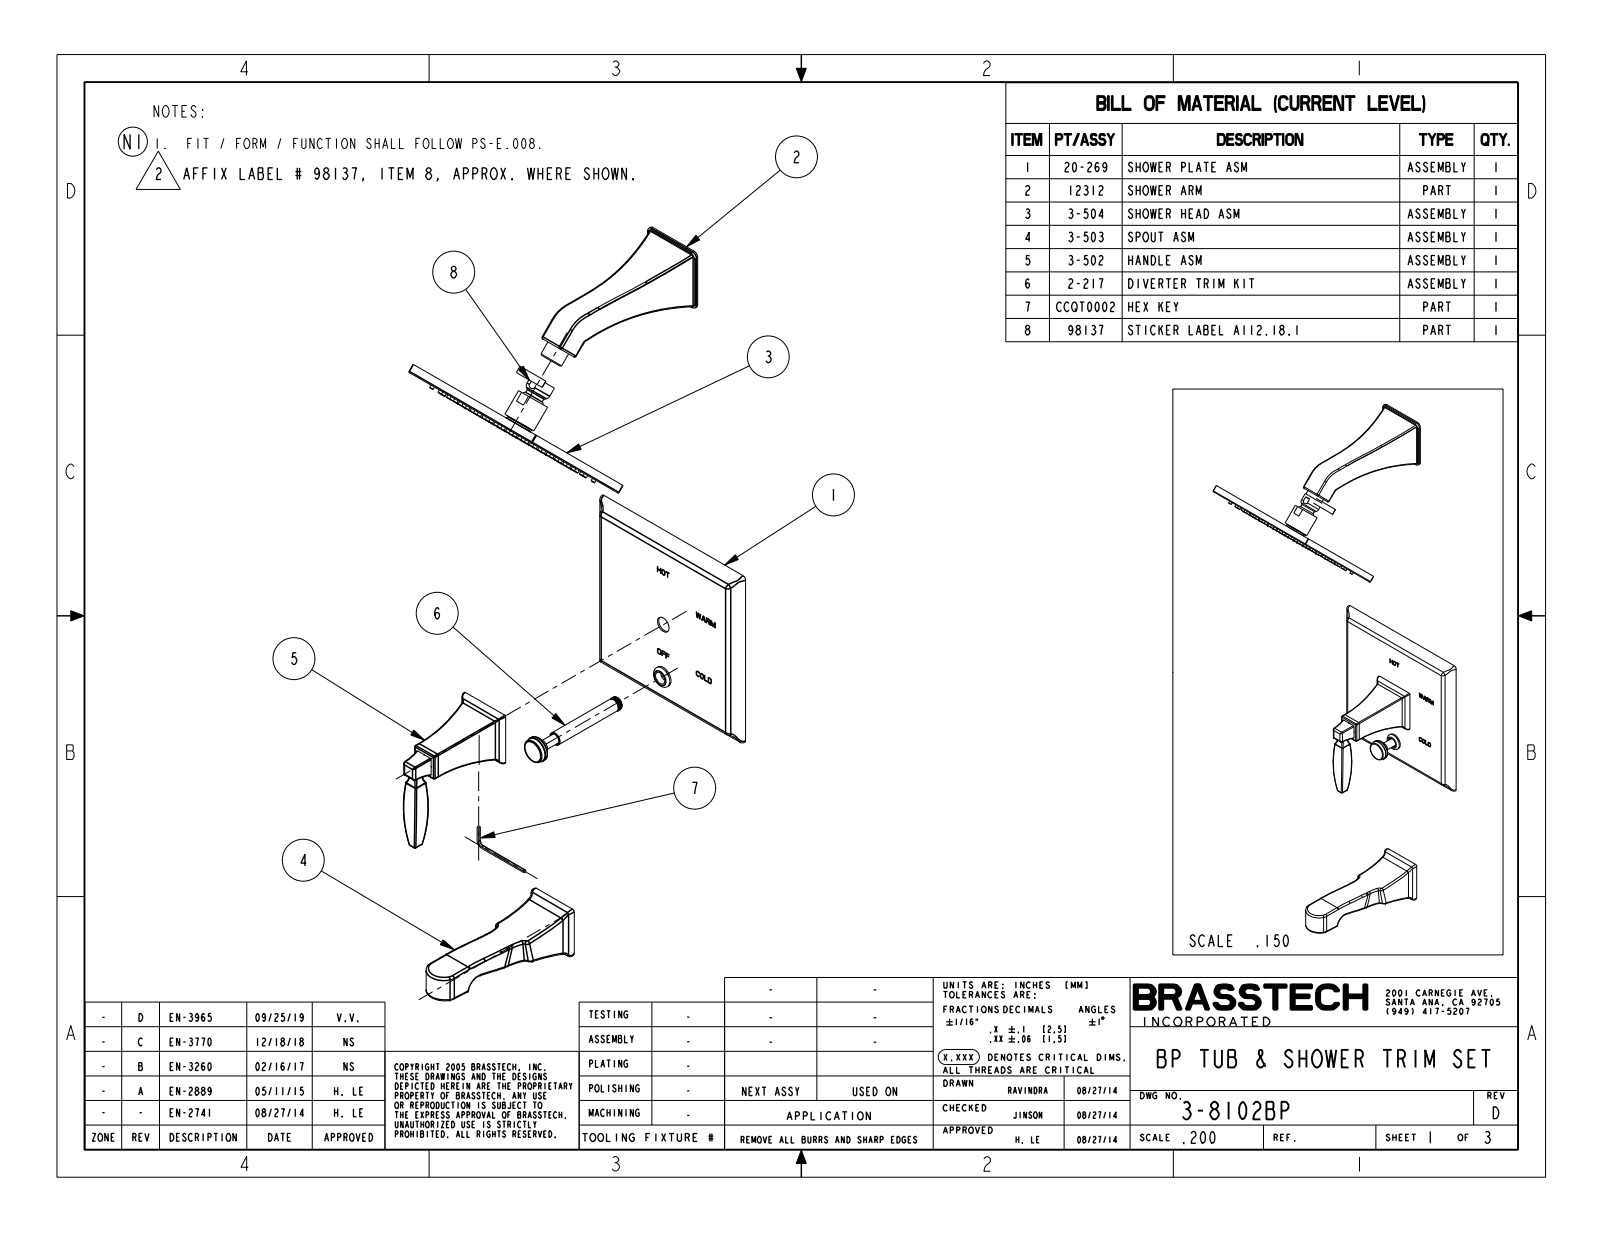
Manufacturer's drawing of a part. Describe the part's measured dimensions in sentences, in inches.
The part is named "NCIP-012_1_AF0; CTWR0281_1_AF0; 91033; 3-501_AF0_ASM (+8 more)". Its 3-D file was written by "PRO/ENGINEER BY PARAMETRIC TECHNOLOGY CORPORATION, 2013150 (CONFIG_CONTROL_DESIGN)". It is 27 solids with 2310 faces: 862 planar, 704 cylindrical and 744 other. Overall it measures 26.778 by 11.664 by 7 inches. Its volume is 28.19 cubic inches and its surface area 437.5 square inches. Round holes: 2 of diameter 0.591, 2 of diameter 0.945, 1 of diameter 0.13, 1 of diameter 0.15, 1 of diameter 0.156, 1 of diameter 0.165, 1 of diameter 0.189, 1 of diameter 0.197, 1 of diameter 0.265, 1 of diameter 0.288, 1 of diameter 0.318, 1 of diameter 0.335. Round bosses or shafts: 2 of diameter 1.339, 1 of diameter 1.11, 1 of diameter 1.043, 1 of diameter 0.984, 1 of diameter 0.945, 1 of diameter 0.9, 1 of diameter 0.886, 1 of diameter 0.866. Partial cylindrical surfaces (rounded edges, fillets, slot ends): 100 of radius 0.008, 40 of radius 0.039, 30 of radius 0.004, 22 of radius 0.079, 15 of radius 0.015, 8 of radius 0.157, 8 of radius 0.197, 4 of radius 0.062. The main face-to-face distances are 0.315, 0.059, 0.5, 0.441, 0.197, 0.244, 0.303, 5.945, 0.11, 1.181. The hole center spacings are 2.175, 7.668, 9.843, 14.795, 16.97, 24.638.
